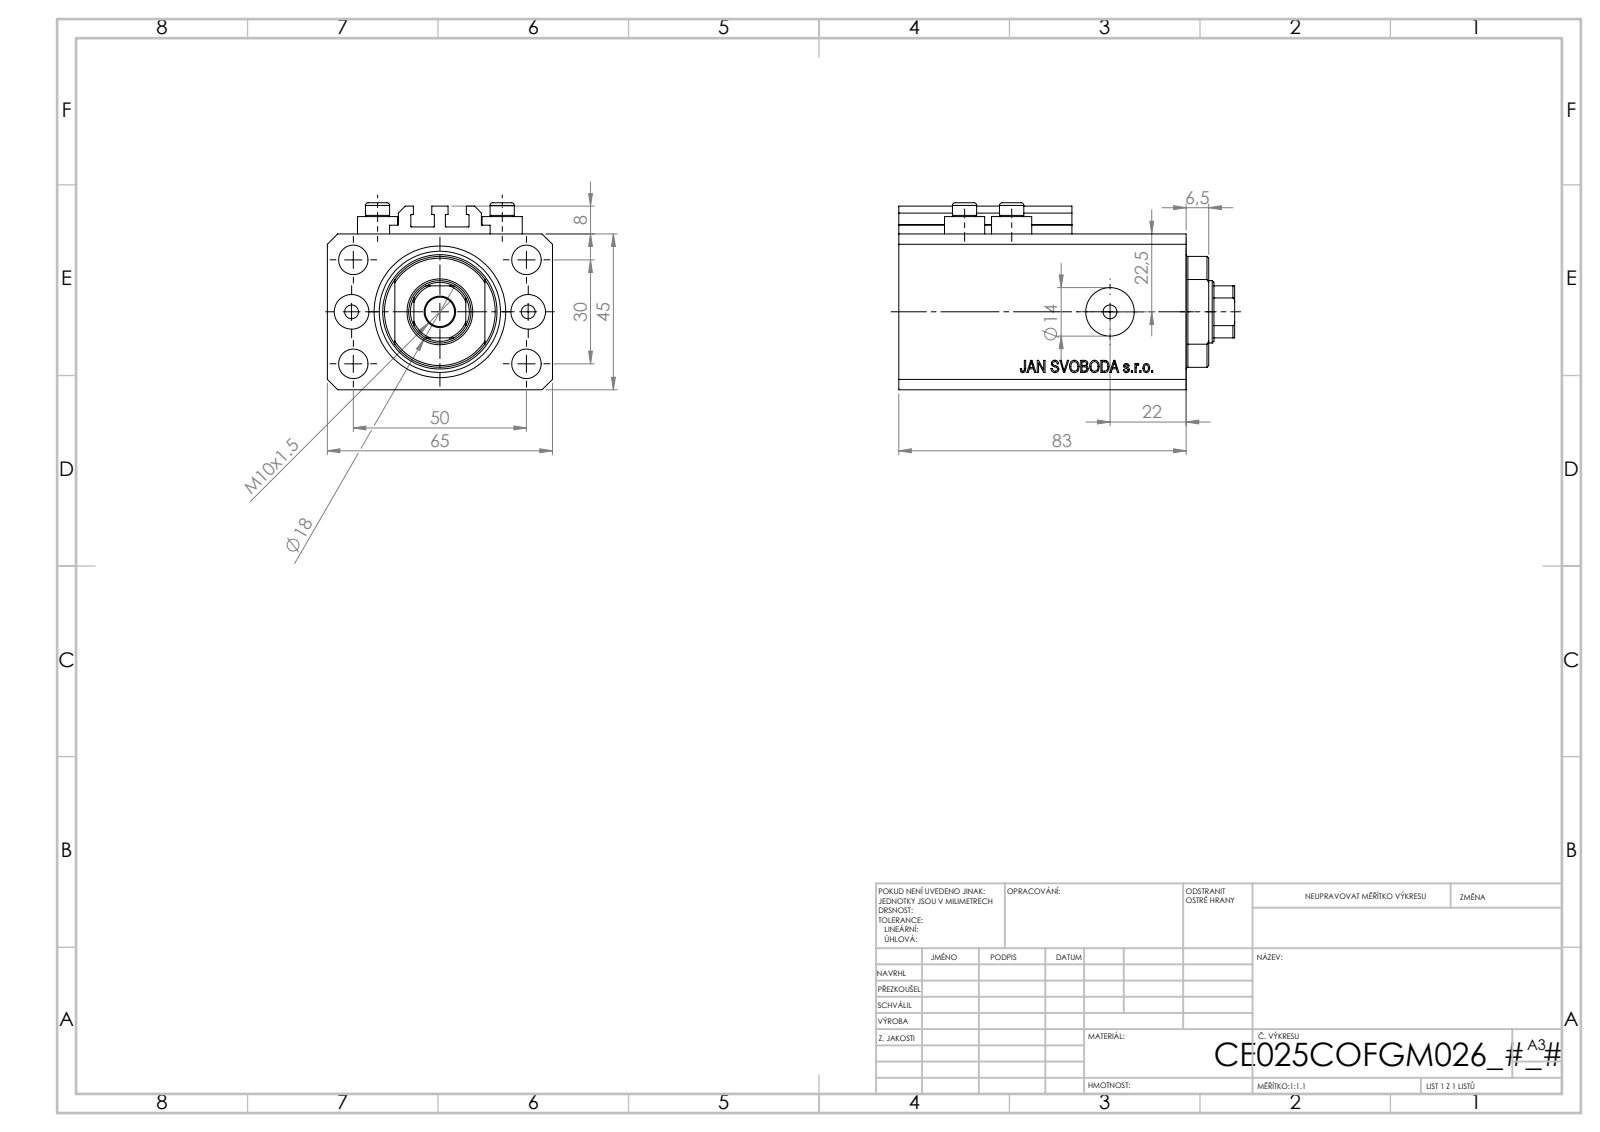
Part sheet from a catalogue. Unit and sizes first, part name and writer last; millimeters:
Units: millimetres
Overall size (bounding box): 97 × 65 × 54
Round holes (diameter × count): ⌀4 ×8, ⌀8.5 ×5, ⌀10 ×2, ⌀14 ×2, ⌀18 ×1, ⌀25 ×1, ⌀38 ×1
Round bosses / shafts (diameter × count): ⌀11.6 ×4, ⌀7 ×4
Partial cylindrical surfaces — rounded edges, fillets, slot ends (radius × count): R0.2 ×10, R8.5 ×1, R16 ×1
Main face-to-face distances: 45, 65, 14, 69, 83, 47, 6.9, 62.1, 76.1, 3
Hole centre spacings: 15.01, 29.15, 52.68, 13.6, 25.5, 30, 36, 38.48
Volume: 227 358 mm³ · Surface area: 60 600 mm²
Bodies: 8 solids, 1034 faces (504 planar, 86 cylindrical, 444 other)
Part name (STEP PRODUCT): V250CE_C_VCP; V250CE_C_Body; V250CE_VC_C; ALLEN BOLT V250CE
STEP written by: SolidWorks 2019 (CONFIG_CONTROL_DESIGN)
